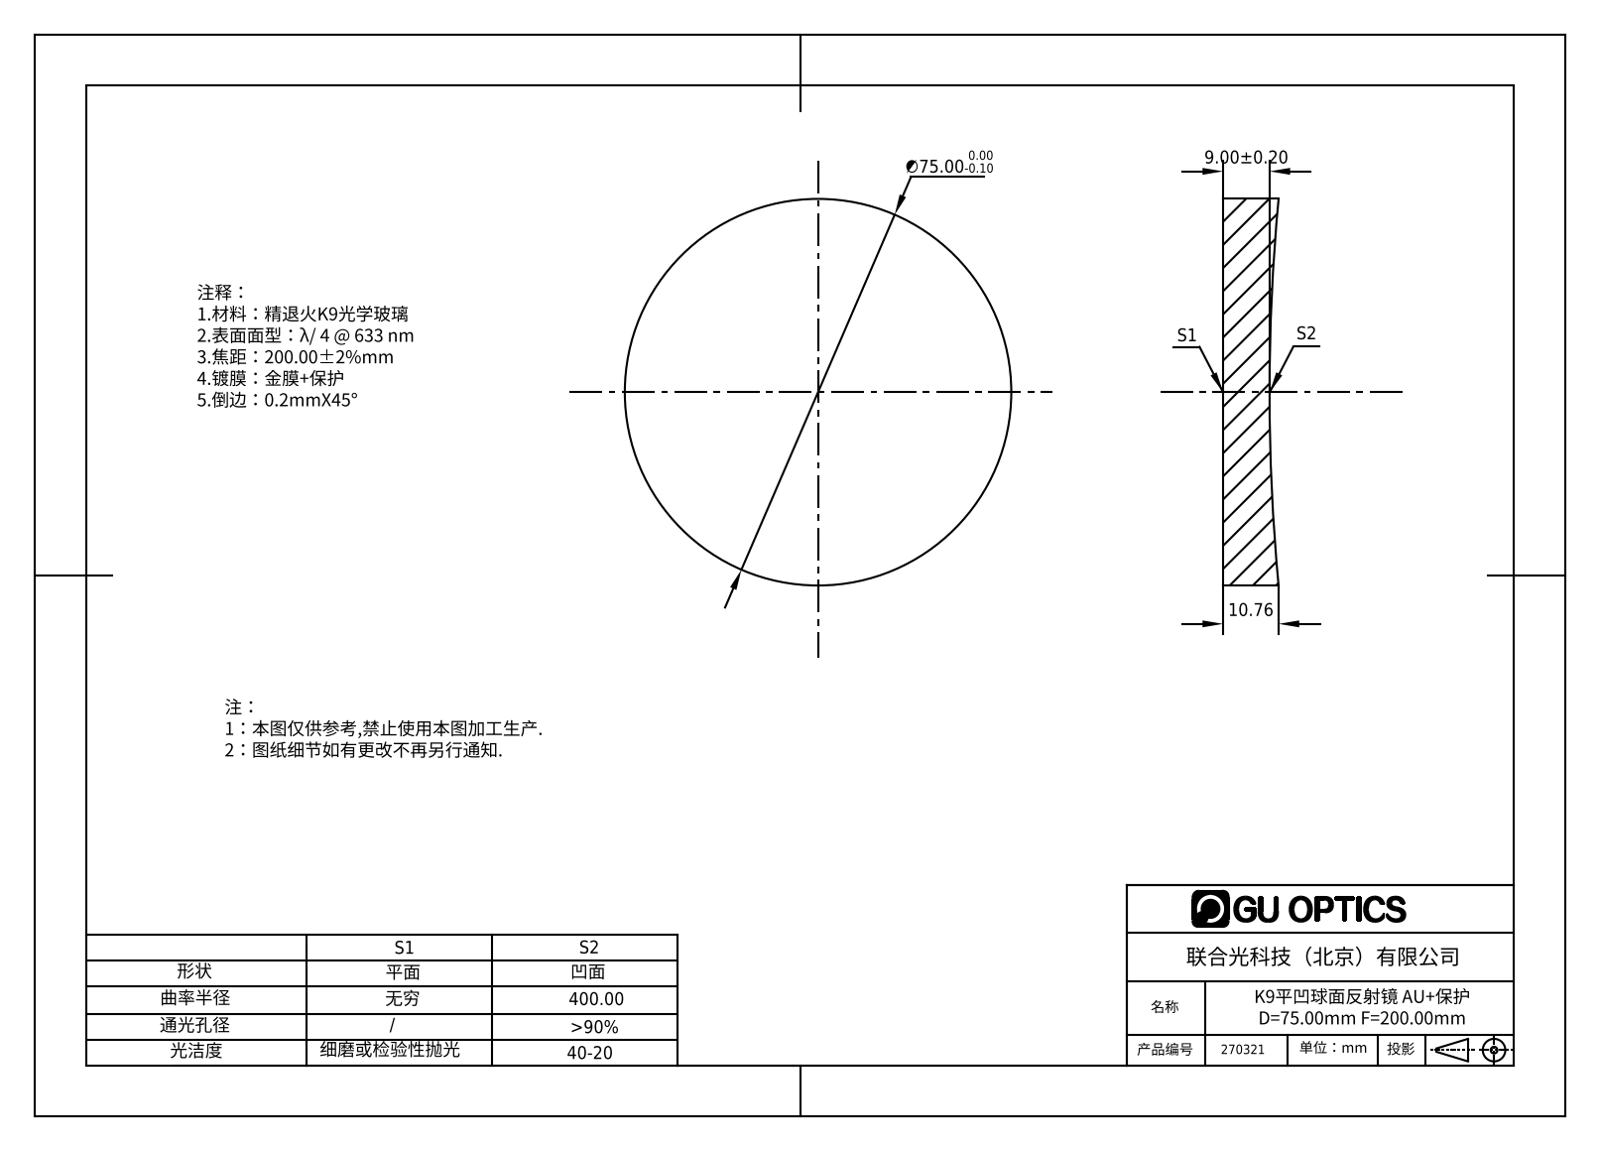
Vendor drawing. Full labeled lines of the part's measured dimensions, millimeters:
Part name (STEP PRODUCT): 270061
STEP written by: SolidWorks 2016 (AUTOMOTIVE_DESIGN)
Units: millimetres
Bodies: 1 solid, 5 faces (1 planar, 2 cylindrical, 2 other)
Overall size (bounding box): 75 × 75 × 10.76
Volume: 43 649 mm³ · Surface area: 11 381 mm²
Round bosses / shafts (diameter × count): ⌀75 ×1
